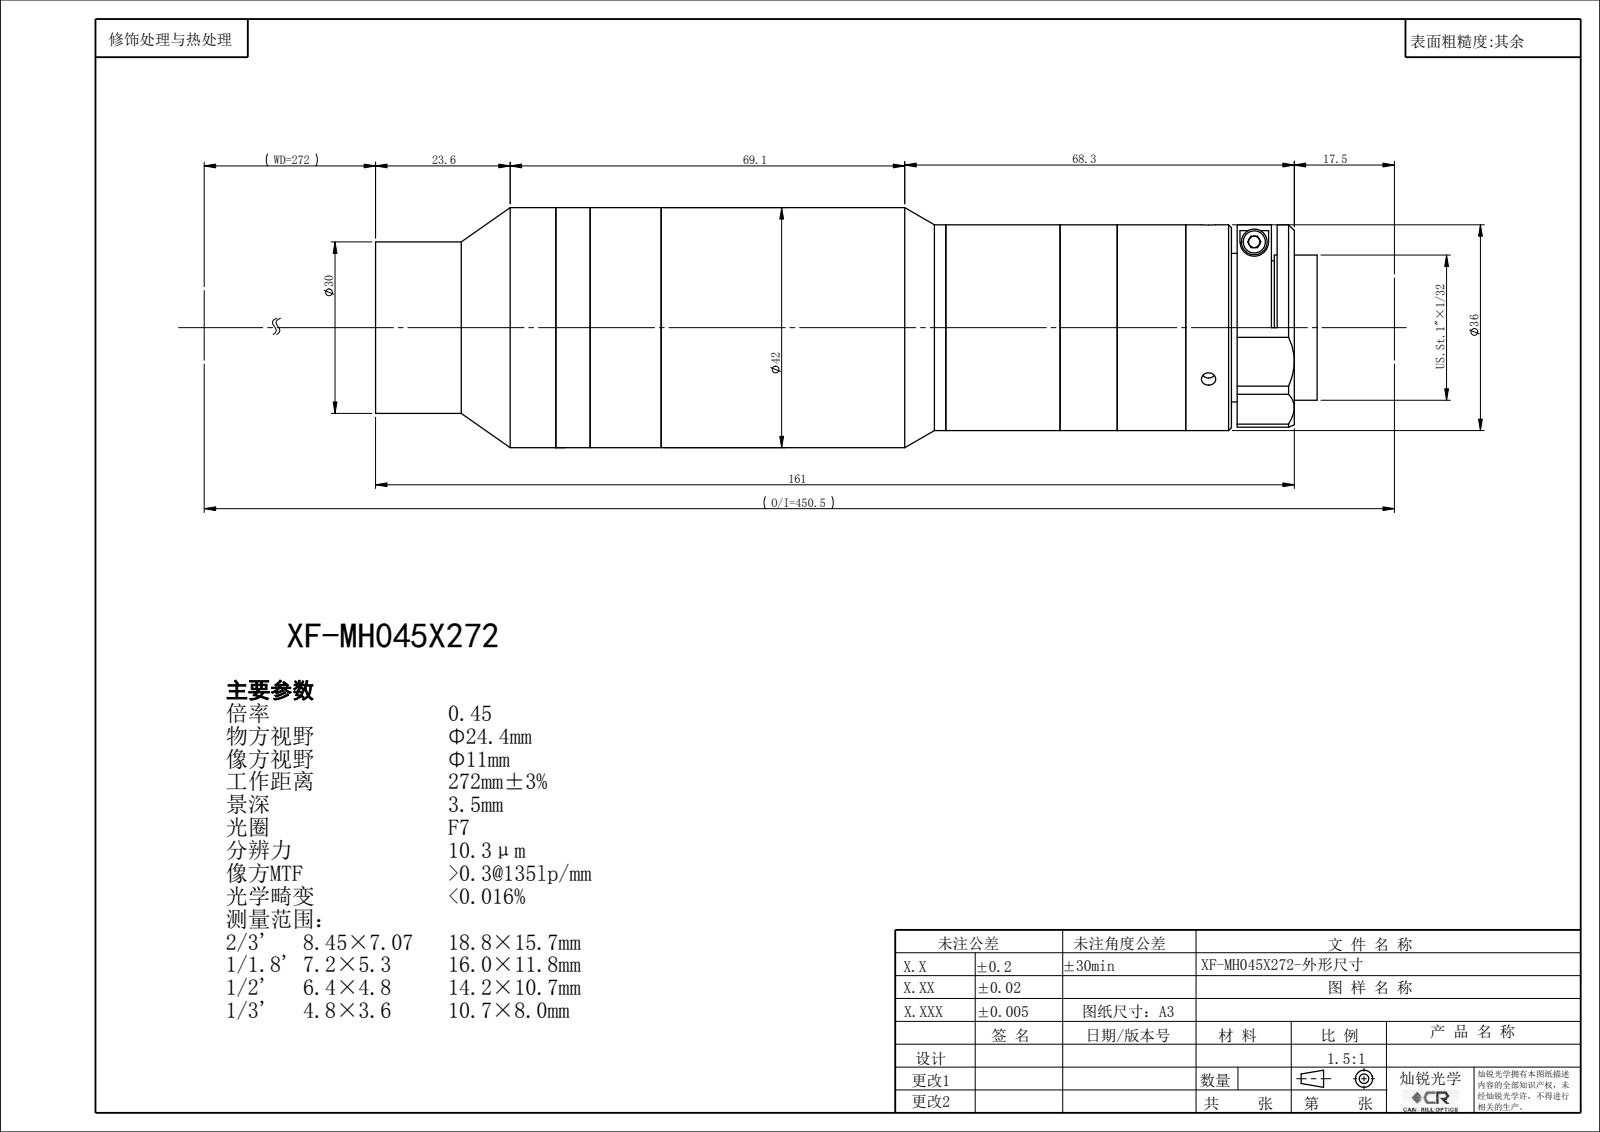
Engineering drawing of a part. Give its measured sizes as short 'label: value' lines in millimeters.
name: XF-MH045X272
written by: SolidWorks 2022 (CONFIG_CONTROL_DESIGN)
unit: mm
bodies: 0 solids, 135 faces (65 planar, 46 cylindrical, 24 other)
size: 164.95 × 42 × 42
holes: 3× ⌀2.5, 1× ⌀22.4, 1× ⌀24, 1× ⌀26.4
bosses: 1× ⌀42, 1× ⌀36, 1× ⌀34, 1× ⌀30, 1× ⌀25.4
face distances: 1.5, 59.62, 61.12, 20, 39.62, 41.12, 48, 28, 11.62, 13.12
